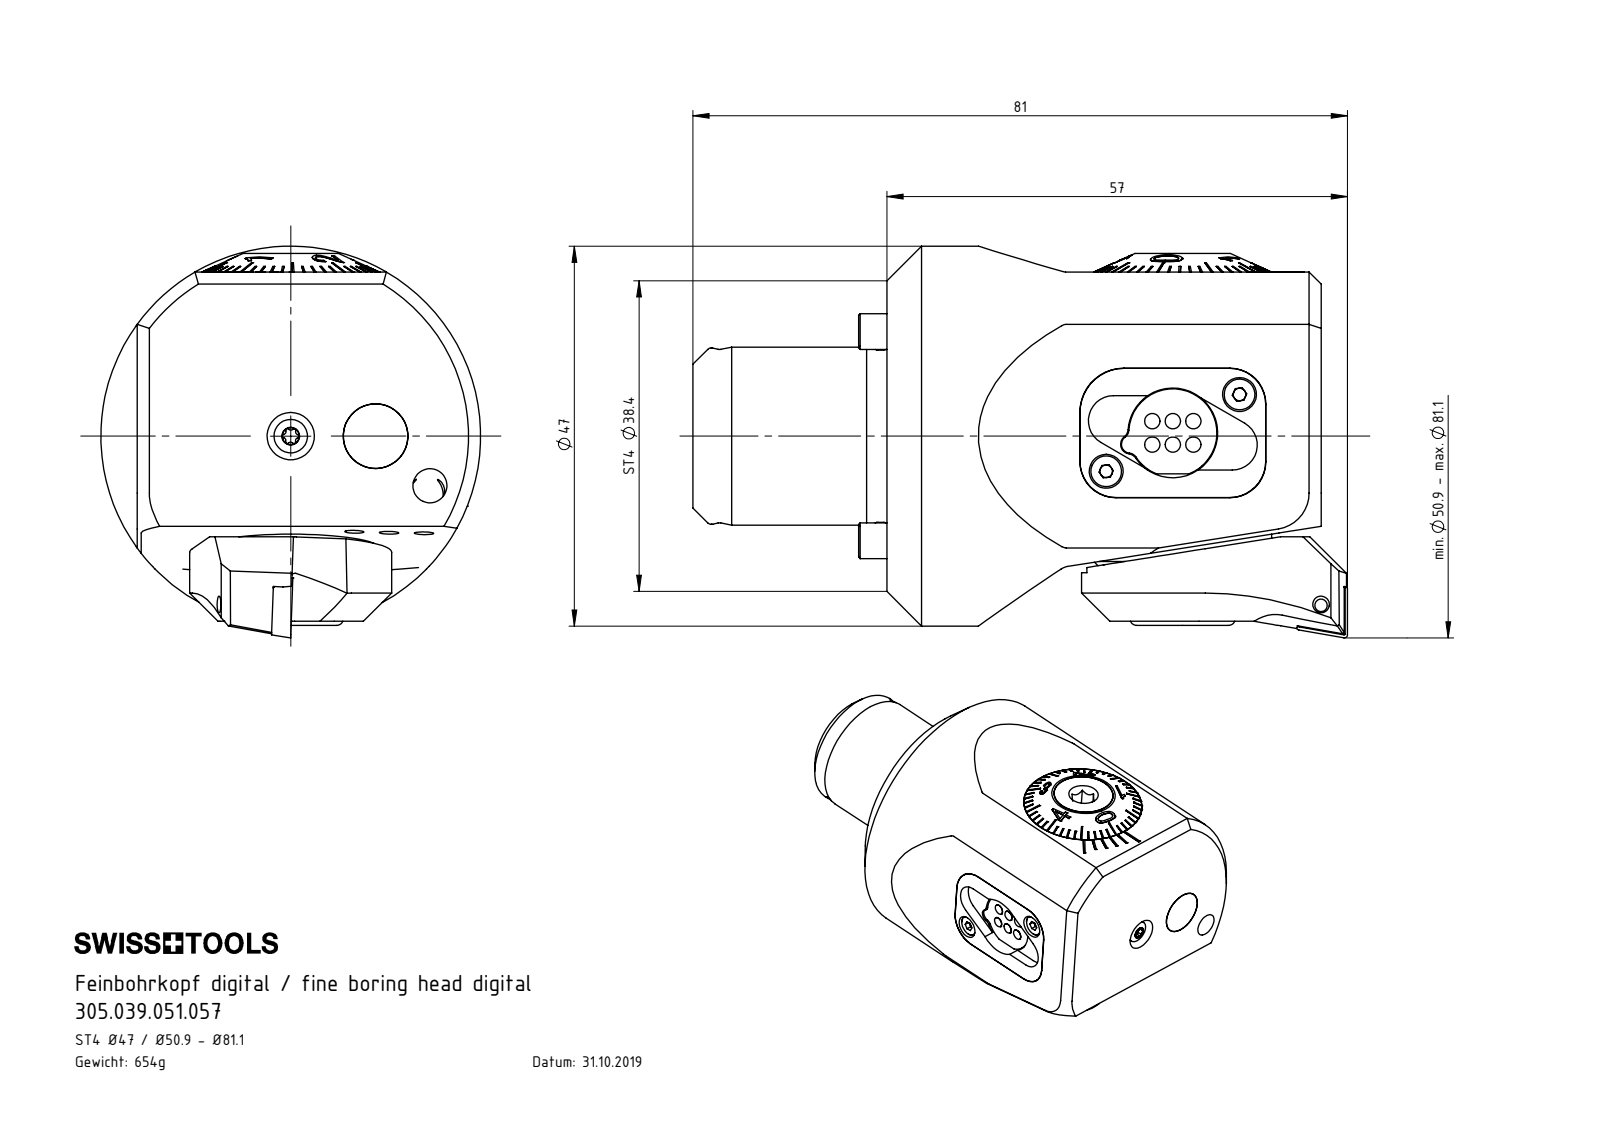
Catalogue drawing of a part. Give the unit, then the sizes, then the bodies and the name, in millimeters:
Units: millimetres
Overall size (bounding box): 81 × 45.8 × 42
Round holes (diameter × count): ⌀3.3 ×4, ⌀1.6 ×2, ⌀2.2 ×2, ⌀2.5 ×2, ⌀3.5 ×2, ⌀4.2 ×2, ⌀6.8 ×2, ⌀8.5 ×2, ⌀2.05 ×1, ⌀2.1 ×1, ⌀2.8 ×1, ⌀3 ×1
Round bosses / shafts (diameter × count): ⌀1.9 ×6, ⌀8 ×2, ⌀3.8 ×2, ⌀2 ×2, ⌀42 ×1, ⌀22 ×1, ⌀21.98 ×1, ⌀21.9 ×1
Partial cylindrical surfaces — rounded edges, fillets, slot ends (radius × count): R0.5 ×9, R1.2 ×8, R0.21 ×6, R1.1 ×6, R0.36 ×5, R3.2 ×5, R4.5 ×4, R4.4 ×3
Main face-to-face distances: 53.75, 27.7, 4.5, 4, 5.6, 34.7, 2.3, 1.1, 2, 2.2
Hole centre spacings: 9.52, 13.2, 16.87, 3.84, 4, 7.67, 10.5, 15.38
Volume: 75 022 mm³ · Surface area: 30 422 mm²
Bodies: 26 solids, 1058 faces (439 planar, 254 cylindrical, 365 other)
Part name (STEP PRODUCT): F42-BG1.DA2.022_Standard min; F42-WCA.001.009_C_fertigbearbeitet; ST4.F42.DA2.057; Fxx-MAB.xxx.xxx_A_F42 (+8 more)
STEP written by: SolidWorks 2017 (CONFIG_CONTROL_DESIGN)
